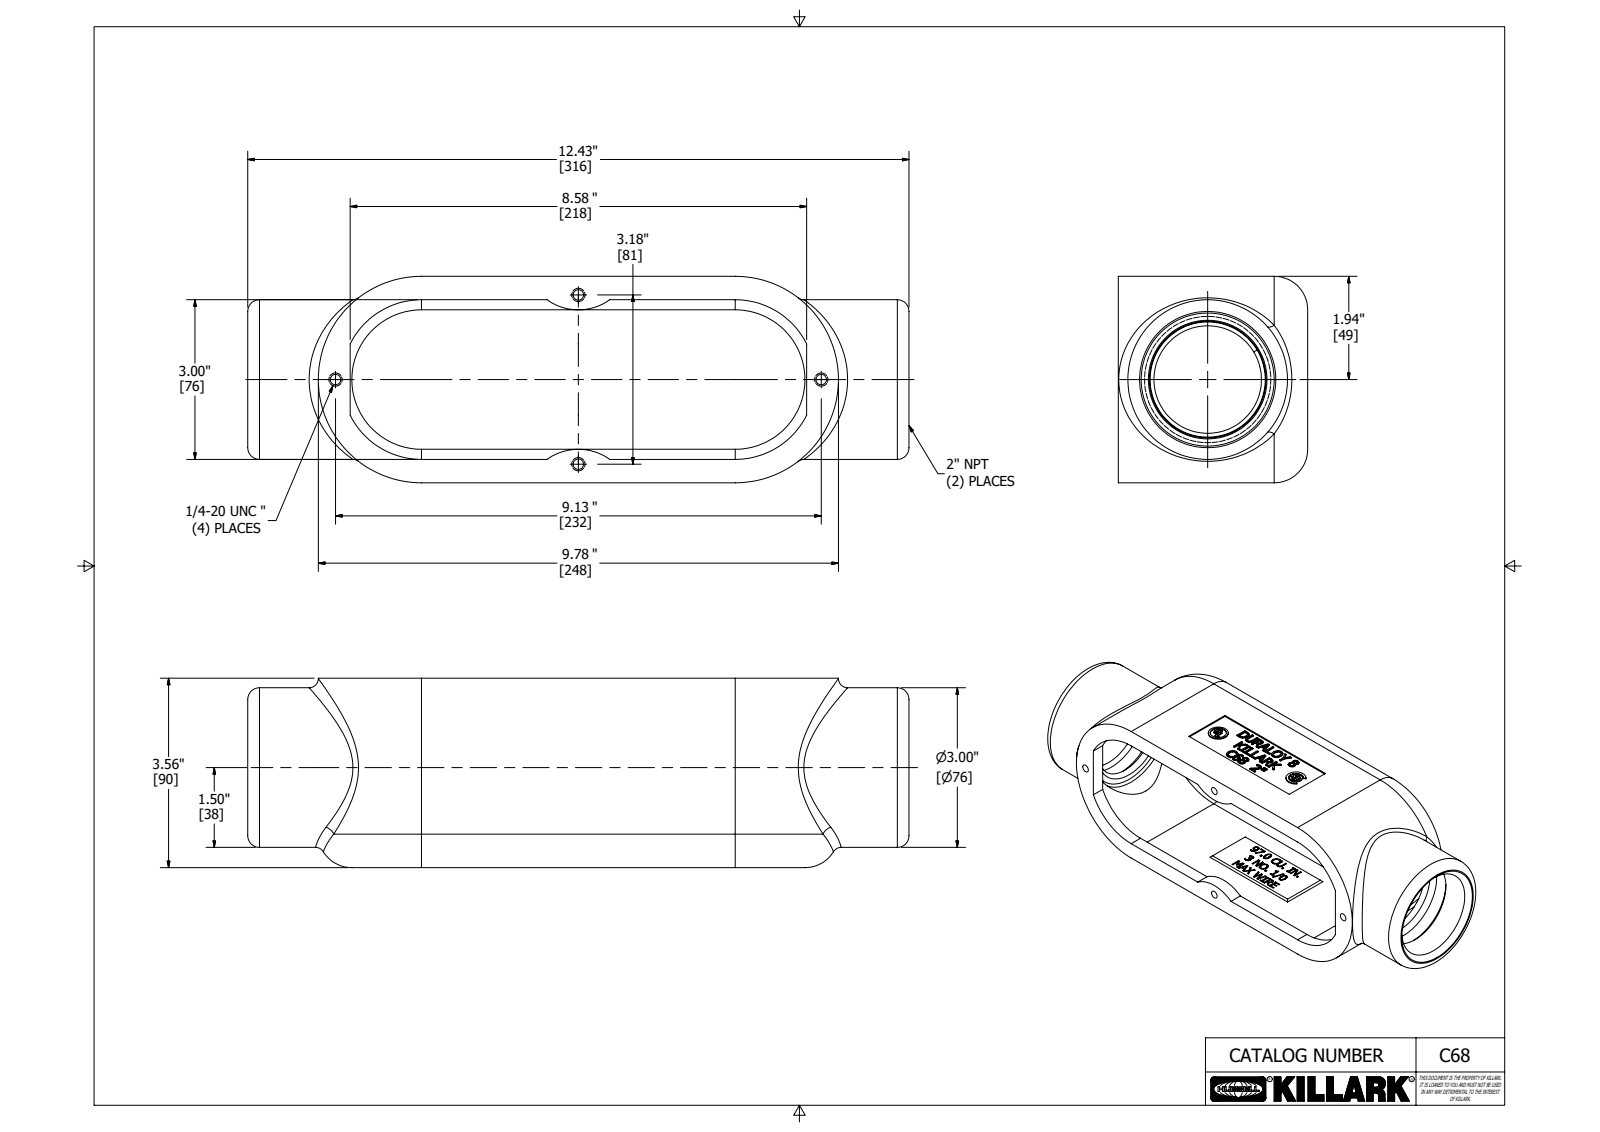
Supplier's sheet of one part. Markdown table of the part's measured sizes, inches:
| quantity | value |
| --- | --- |
| part name | 21711-2 |
| STEP written by | Autodesk Inventor 2018 (AUTOMOTIVE_DESIGN) |
| units | inches |
| bodies | 1 solid, 740 faces (436 planar, 40 cylindrical, 264 other) |
| overall size | 12.429 × 3.88 × 3.56 |
| volume | 30.63 in³ |
| surface area | 272.1 in² |
| round holes (diameter × count) | 0.196 × 4, 0.407 × 1, 2.381 × 1 |
| round bosses / shafts (diameter × count) | 3 × 1, 0.5 × 1 |
| partial cylindrical surfaces (radius × count) | 0.43 × 2, 0.63 × 2, 1.011 × 2, 1.5 × 2, 1.74 × 2, 1.94 × 2, 0.016 × 1, 0.063 × 1 |
| main face-to-face distances | 0.2, 3.68, 3.88, 3.48, 3.56, 3.36, 3.23, 3.03, 0.33, 3.85 |
| hole center spacings | 4.834, 3.18, 9.13 |
